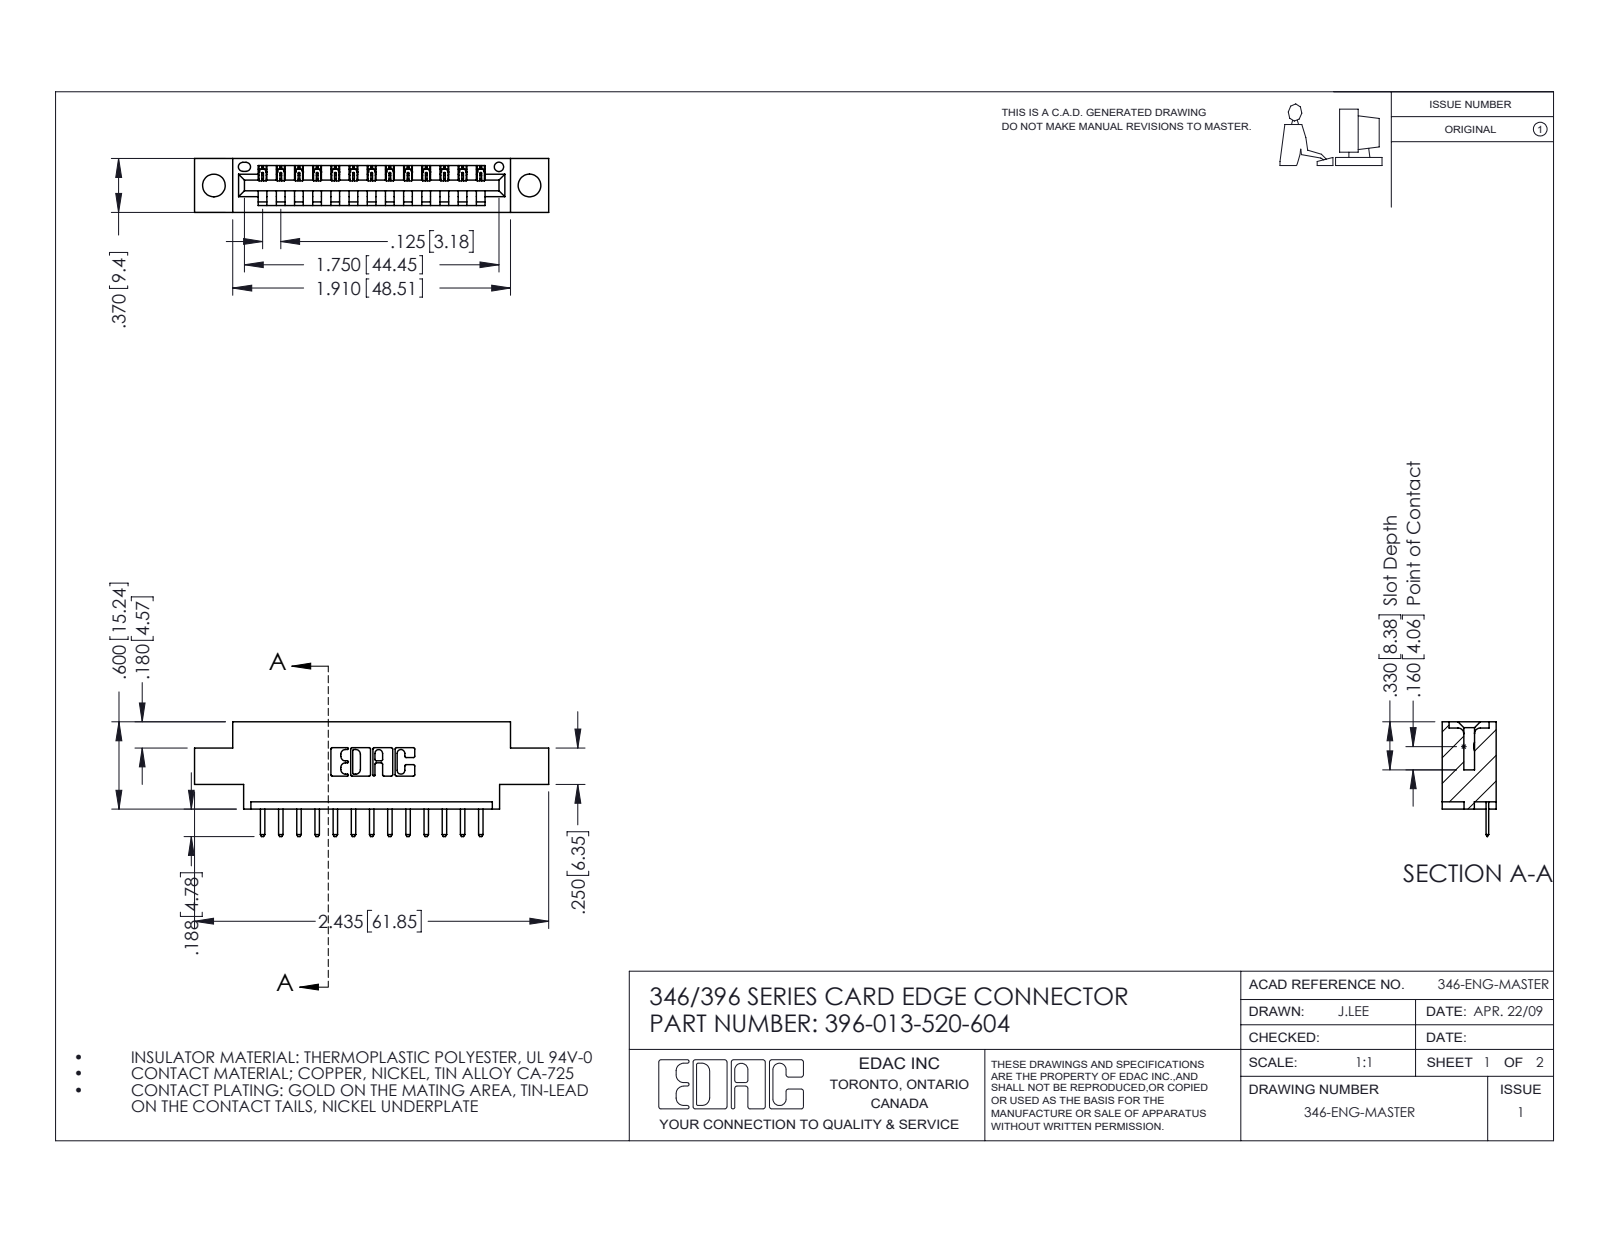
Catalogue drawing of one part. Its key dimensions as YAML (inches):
part_name: "396-013-520-604; 346 Part_0.170 Offset - 0.156 Dia-TH; 345-292-001_345-293-120"
step_written_by: "SolidWorks 2016 (CONFIG_CONTROL_DESIGN)"
units: inches
bodies: {solids: 14, faces: 932, planar: 626, cylindrical: 306, other: 0}
overall_size: [2.435, 0.788, 0.37]
volume: 0.332
surface_area: 9.808
round_holes:
  - {diameter: 0.156, count: 2}
  - {diameter: 0.064, count: 1}
partial_cylinders:
  - {radius: 0.01, count: 28}
  - {radius: 0.006, count: 26}
  - {radius: 0.01, count: 22}
  - {radius: 0.007, count: 6}
  - {radius: 0.031, count: 6}
  - {radius: 0.026, count: 3}
  - {radius: 0.031, count: 2}
  - {radius: 0.04, count: 2}
face_to_face_distances: [0.37, 0.25, 0.048, 0.322, 0.148, 0.222, 0.1, 0.174, 0.072, 0.298]
hole_center_spacings: [0.246, 1.964, 2.17]
